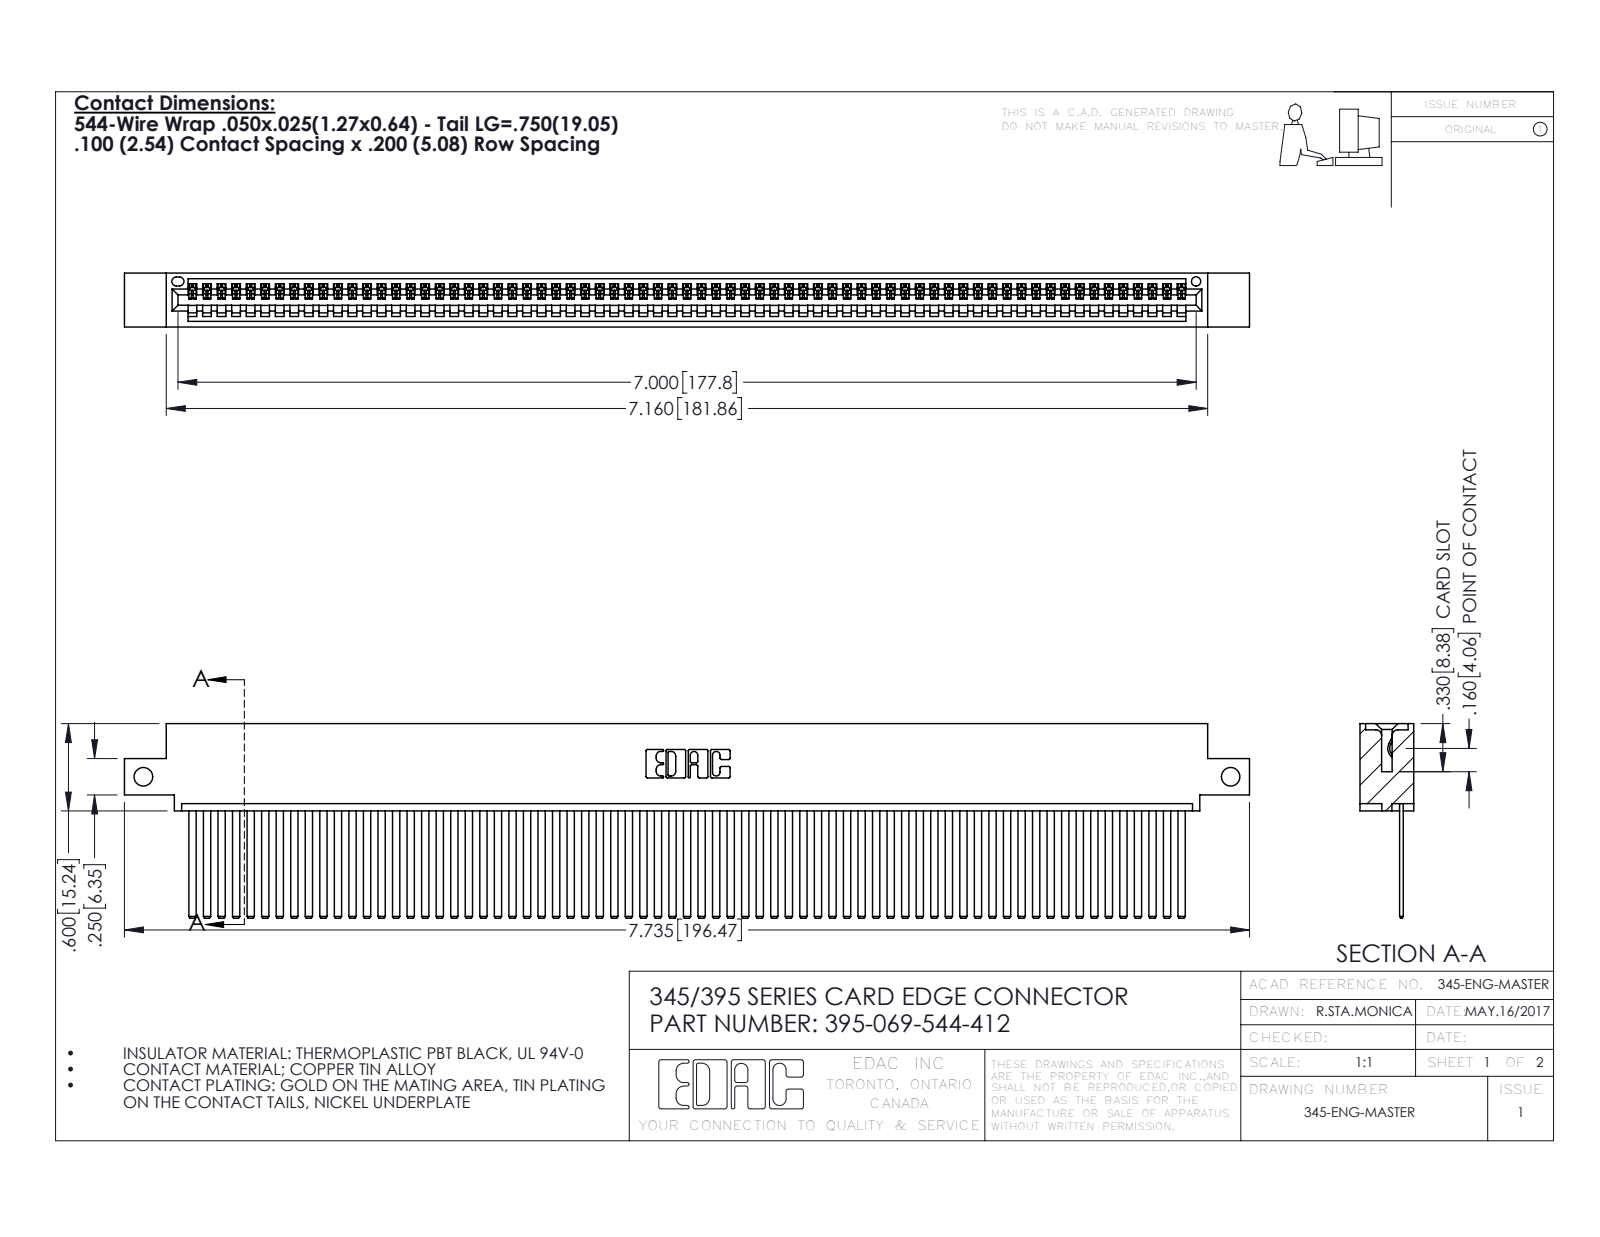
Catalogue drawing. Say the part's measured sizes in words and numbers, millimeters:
The part is named "345 Part_0.110 Offset - Side Mount; 395-069-544-412; 345-292-001_345-293-144". Its 3-D file was written by "SolidWorks 2016 (CONFIG_CONTROL_DESIGN)". It is 70 solids with 3718 faces: 2568 planar, 1150 cylindrical and 0 other. Overall it measures 196.5 by 34 by 9.4 millimeters. Its volume is 19 520 cubic millimeters and its surface area 28 650 square millimeters. Round holes: 2 of diameter 3.3, 1 of diameter 1.6. Partial cylindrical surfaces (rounded edges, fillets, slot ends): 138 of radius 0.2, 22 of radius 0.3, 6 of radius 0.2, 6 of radius 0.8, 3 of radius 0.7, 2 of radius 0.8, 2 of radius 1, 1 of radius 0.4. The main face-to-face distances are 1.8, 7.6, 0.6, 2.5, 6.9, 9.4, 5.1, 5.7, 3.8, 1.8. The hole center spacings are 189.9.
